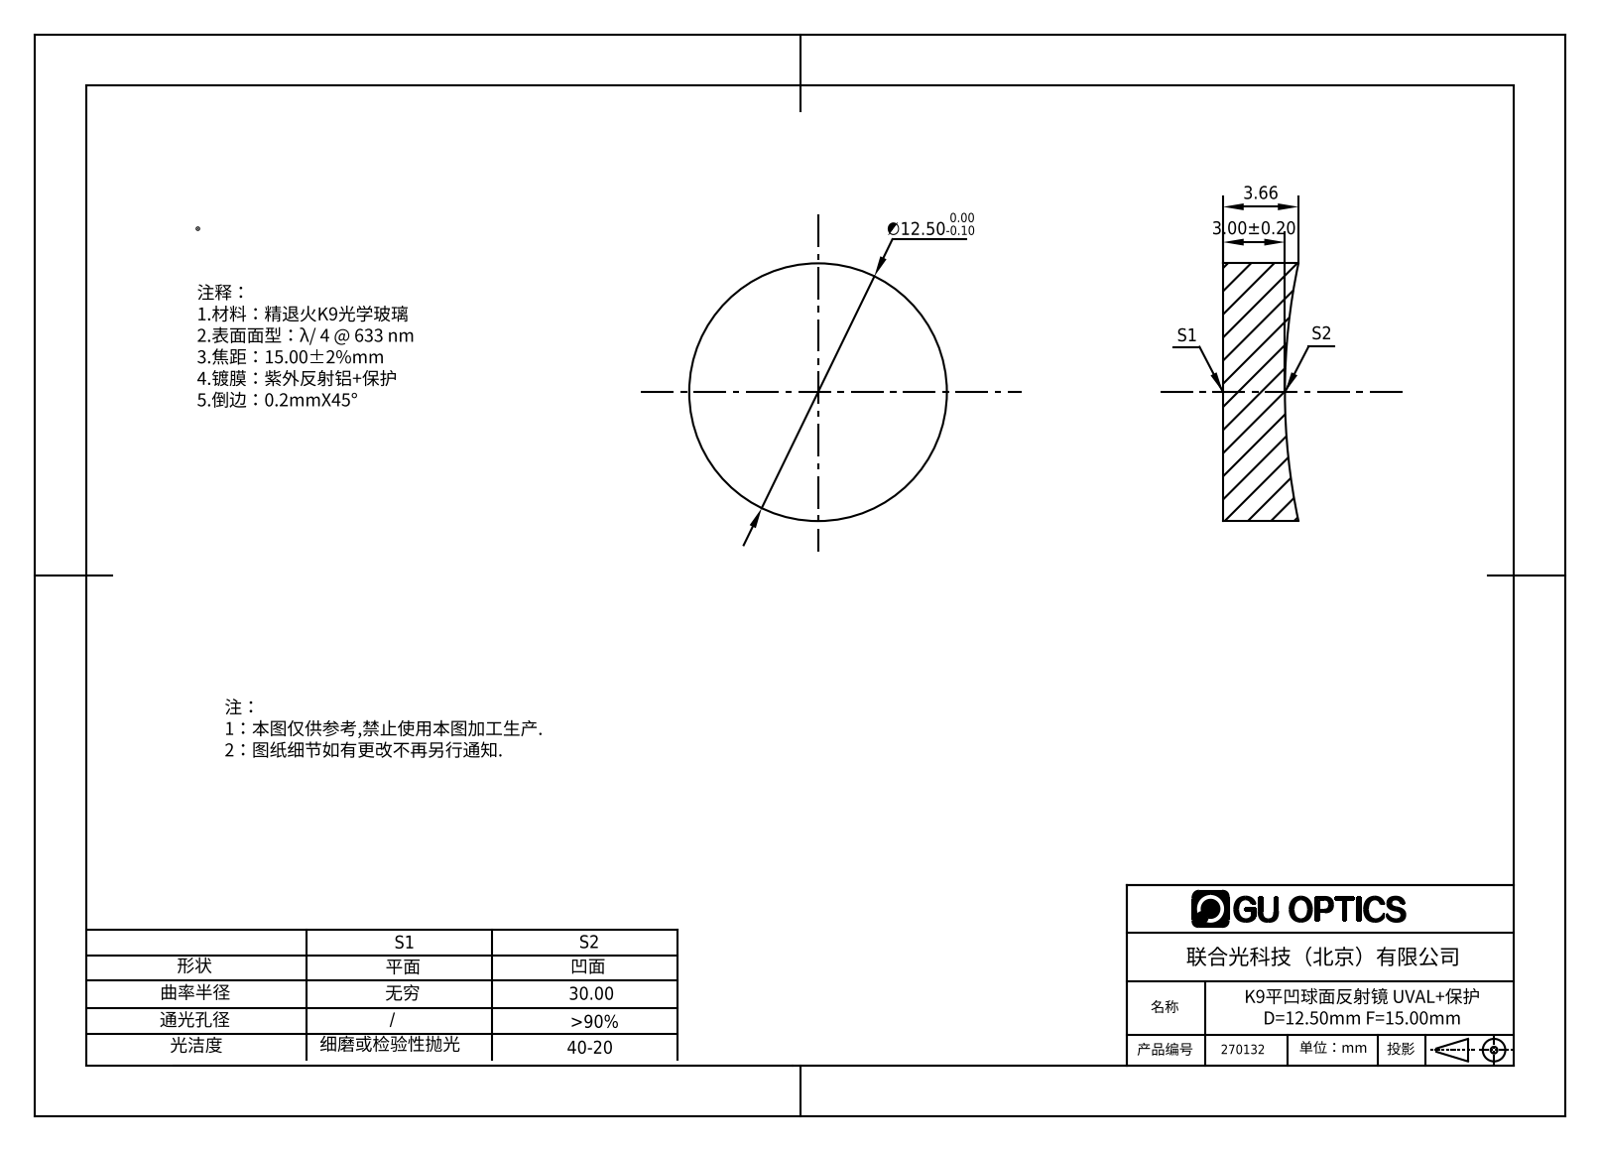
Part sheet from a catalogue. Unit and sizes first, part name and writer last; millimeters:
Units: millimetres
Overall size (bounding box): 12.5 × 12.5 × 3.66
Round bosses / shafts (diameter × count): ⌀12.5 ×1
Volume: 408 mm³ · Surface area: 390 mm²
Bodies: 1 solid, 5 faces (1 planar, 2 cylindrical, 2 other)
Part name (STEP PRODUCT): 270002
STEP written by: SolidWorks 2016 (AUTOMOTIVE_DESIGN)
